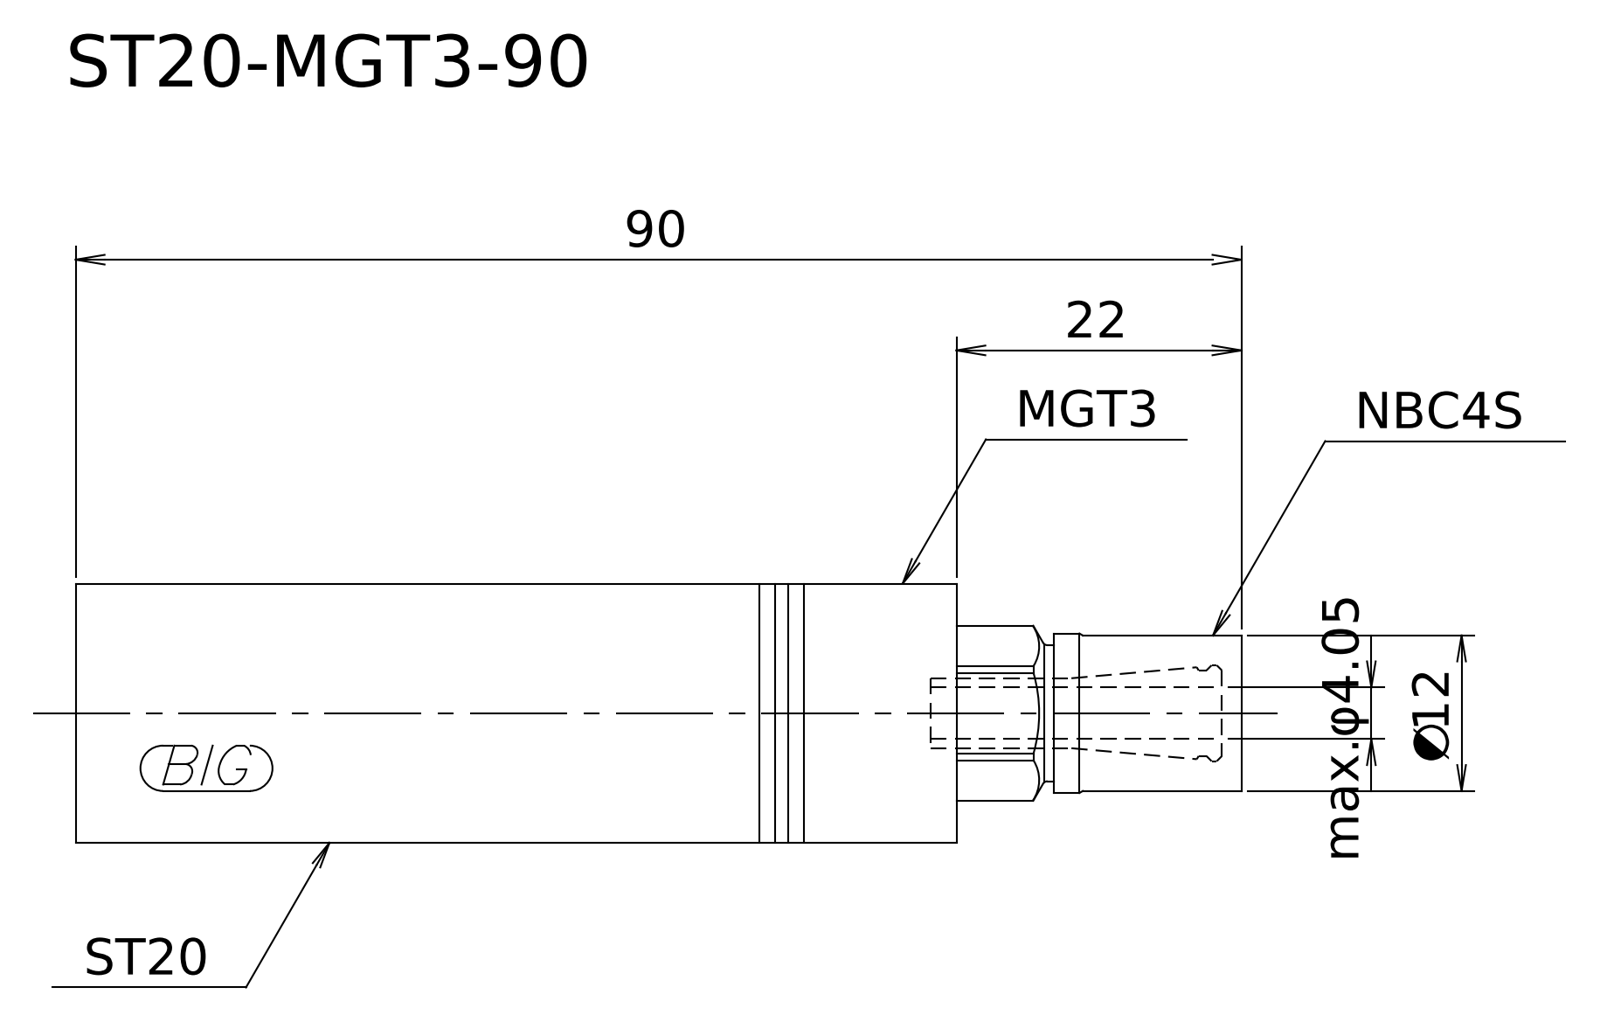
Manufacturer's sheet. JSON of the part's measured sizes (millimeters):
{"step_written_by": "Kubotek KeyCreator 2011 V10.0.2 (22737) (automotive_design)", "units": "millimeters", "bodies": {"solids": 1, "faces": 12, "planar": 4, "cylindrical": 5, "other": 3}, "overall_size": [90, 20, 20], "volume_mm3": 24023, "surface_area_mm2": 5782, "round_bosses_or_shafts": [[20, 1], [13.5, 1], [12.2, 1], [12, 1], [10.5, 1]], "face_to_face_distances": [68, 22, 90, 14.5, 7.5, 75.5]}
